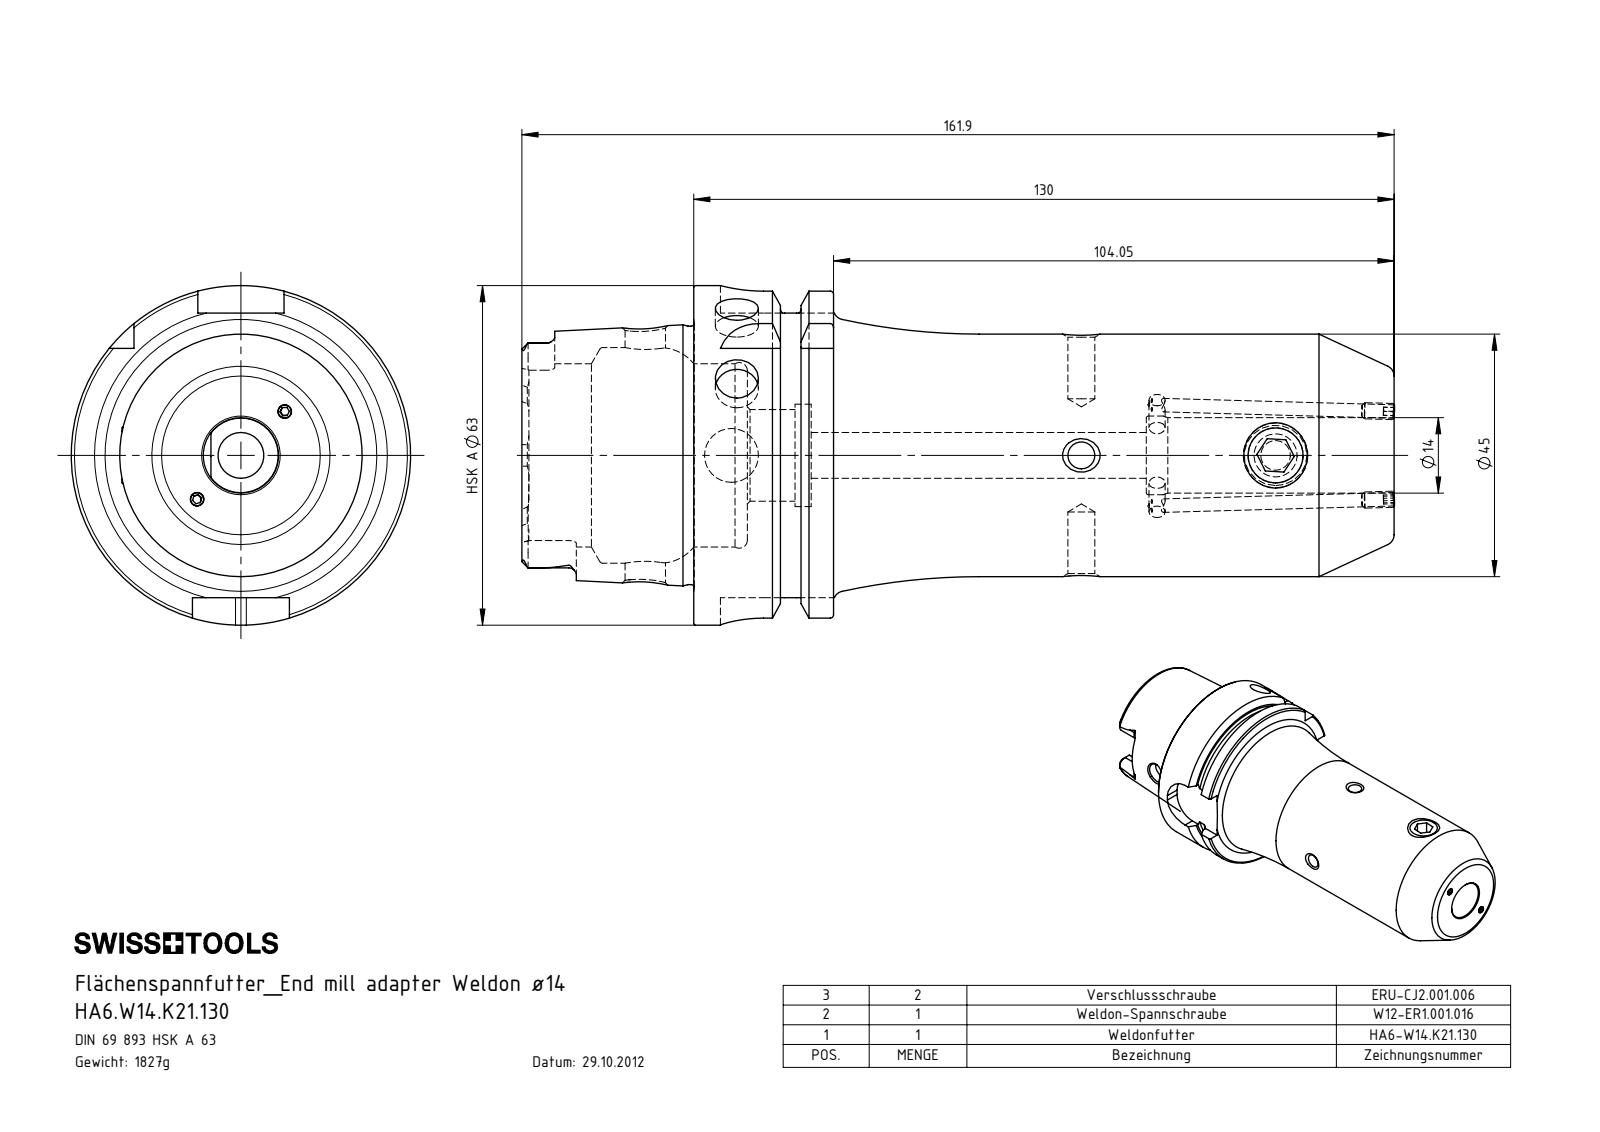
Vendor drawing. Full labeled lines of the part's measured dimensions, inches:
Part name (STEP PRODUCT): HA6-W14.K21.130; ERU-CJ2.001.006; W12-ER1.001.016; HA6-W14.K21.130_A_Fertigbearbeitung
STEP written by: SolidWorks 2012 (CONFIG_CONTROL_DESIGN)
Units: inches
Bodies: 4 solids, 289 faces (78 planar, 81 cylindrical, 130 other)
Overall size (bounding box): 6.377 × 2.48 × 2.48
Volume: 14.2 in³ · Surface area: 65.82 in²
Round holes (diameter × count): ⌀0.098 ×2, ⌀0.197 ×2, ⌀0.315 ×2, ⌀0.118 ×1, ⌀0.295 ×1, ⌀0.335 ×1, ⌀0.394 ×1, ⌀0.404 ×1, ⌀0.551 ×1, ⌀0.575 ×1, ⌀0.669 ×1, ⌀0.748 ×1
Round bosses / shafts (diameter × count): ⌀0.118 ×2, ⌀2.48 ×1, ⌀2.163 ×1, ⌀1.887 ×1, ⌀1.772 ×1, ⌀0.472 ×1
Partial cylindrical surfaces — rounded edges, fillets, slot ends (radius × count): R0.055 ×6, R0.113 ×4, R0.315 ×4
Main face-to-face distances: 0.63, 1.022, 0.392, 5.118, 4.726, 4.096, 1.256, 1.648, 2.278, 6.374
Hole centre spacings: 1.419, 2.557, 3.187, 3.976
